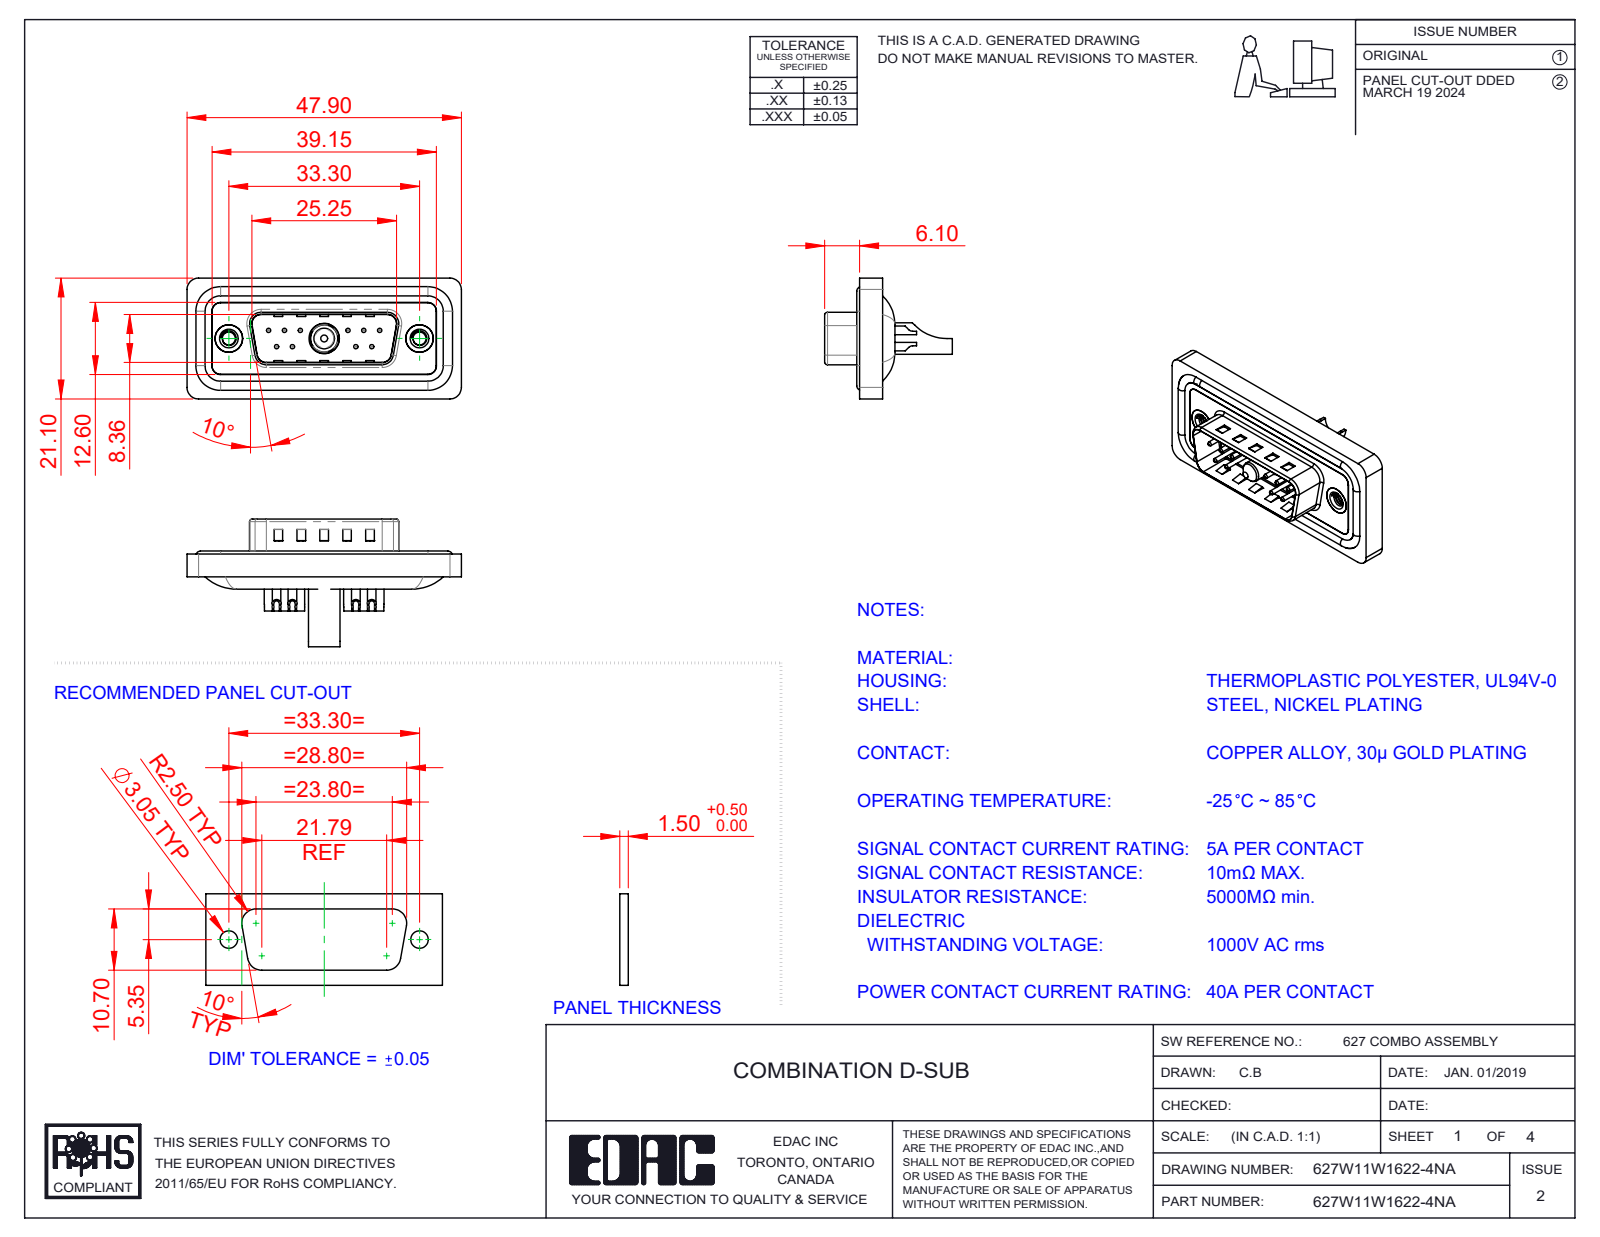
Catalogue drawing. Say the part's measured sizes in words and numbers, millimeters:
The part is named "627Combo Waterproof Housing_15 Contacts; 627Combo Shell Rear_15 Contacts; 627Combo Contact Row 1_22; 627W11W1622-4NA (+5 more)". Its 3-D file was written by "SolidWorks 2023 (CONFIG_CONTROL_DESIGN)". It is 19 solids with 871 faces: 288 planar, 370 cylindrical and 213 other. Overall it measures 47.9 by 22.3 by 21.1 millimeters. Its volume is 5 505 cubic millimeters and its surface area 9 053 square millimeters. Round holes: 10 of diameter 0.75, 10 of diameter 1, 10 of diameter 1.6, 10 of diameter 2, 2 of diameter 2.26, 2 of diameter 4, 2 of diameter 4.8, 2 of diameter 5, 1 of diameter 4.6, 1 of diameter 4.85, 1 of diameter 5.3. Round bosses or shafts: 10 of diameter 1.5, 4 of diameter 1.6, 2 of diameter 4.9, 1 of diameter 5.5, 1 of diameter 5.2, 1 of diameter 4.75, 1 of diameter 3.75, 1 of diameter 3.6. Partial cylindrical surfaces (rounded edges, fillets, slot ends): 26 of radius 1.5, 20 of radius 2, 9 of radius 1, 8 of radius 0.5, 8 of radius 1.6, 4 of radius 0.25, 4 of radius 0.6, 4 of radius 0.65. The main face-to-face distances are 0.4, 1.1, 1.6, 1.5, 0.5, 2.9, 3.1, 2.5, 4.1, 0.82. The hole center spacings are 3.16, 2.77, 13.85, 11.08, 16.62, 5.03, 5.04, 5.54.
